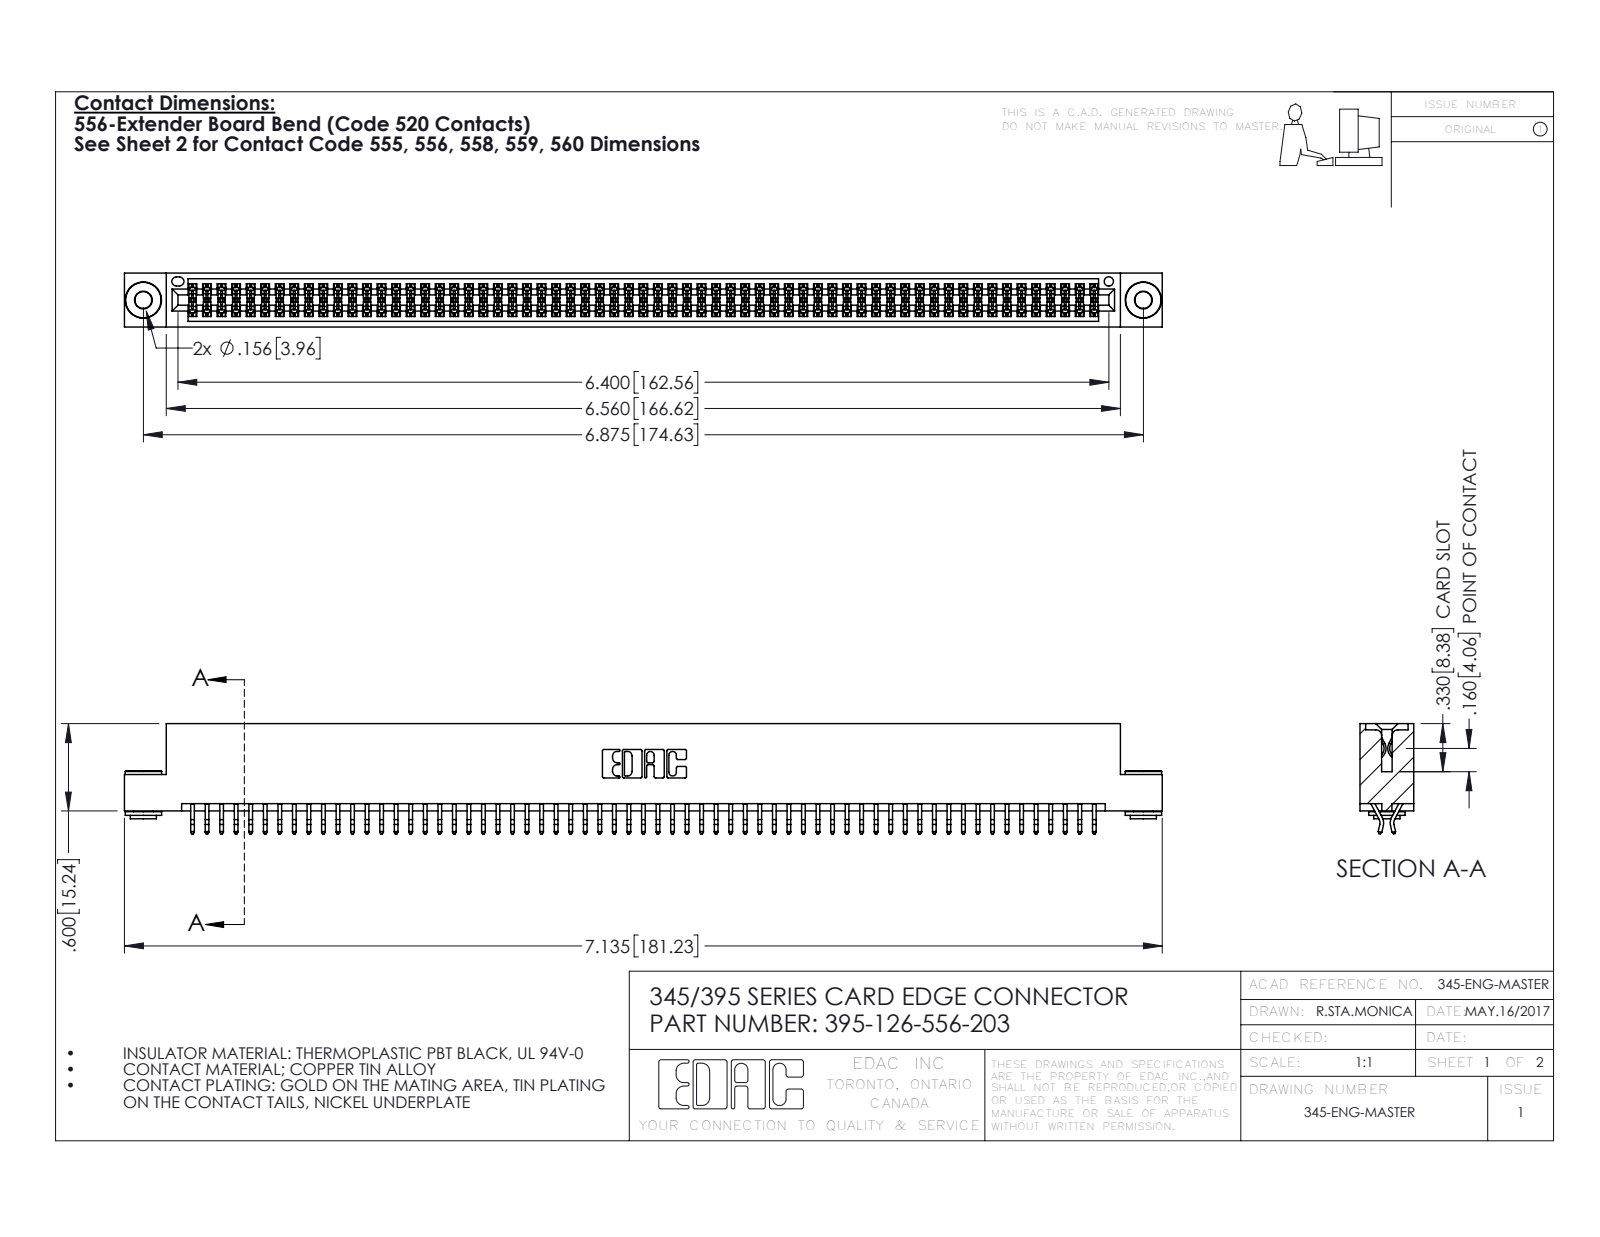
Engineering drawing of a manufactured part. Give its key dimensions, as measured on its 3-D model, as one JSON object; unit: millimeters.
{"part_name": "345-292-001_556 Tail; 345-250-002_345-250-002-102; 345 Part_Flush Mounting Lugs - 0.156 Dia-TH; 395-126-556-203", "step_written_by": "SolidWorks 2016 (CONFIG_CONTROL_DESIGN)", "units": "millimeters", "bodies": {"solids": 129, "faces": 7220, "planar": 4752, "cylindrical": 2460, "other": 8}, "overall_size": [181.2, 19.2, 9.4], "volume_mm3": 17810, "surface_area_mm2": 26830, "round_holes": [[2.9, 2], [4, 2], [1.6, 1]], "round_bosses_or_shafts": [[6.4, 2], [4.6, 2], [3.5, 2]], "partial_cylinders_radius": [[0.2, 189], [0.3, 22], [0.2, 6], [0.8, 6], [0.7, 3], [0.3, 2], [0.4, 2], [0.5, 2]], "face_to_face_distances": [1.8, 7.6, 5.1, 9.4, 0.6, 2.5, 6.9, 5.7, 4.4, 3.8], "hole_center_spacings": [6.9, 168.6, 174.6]}
